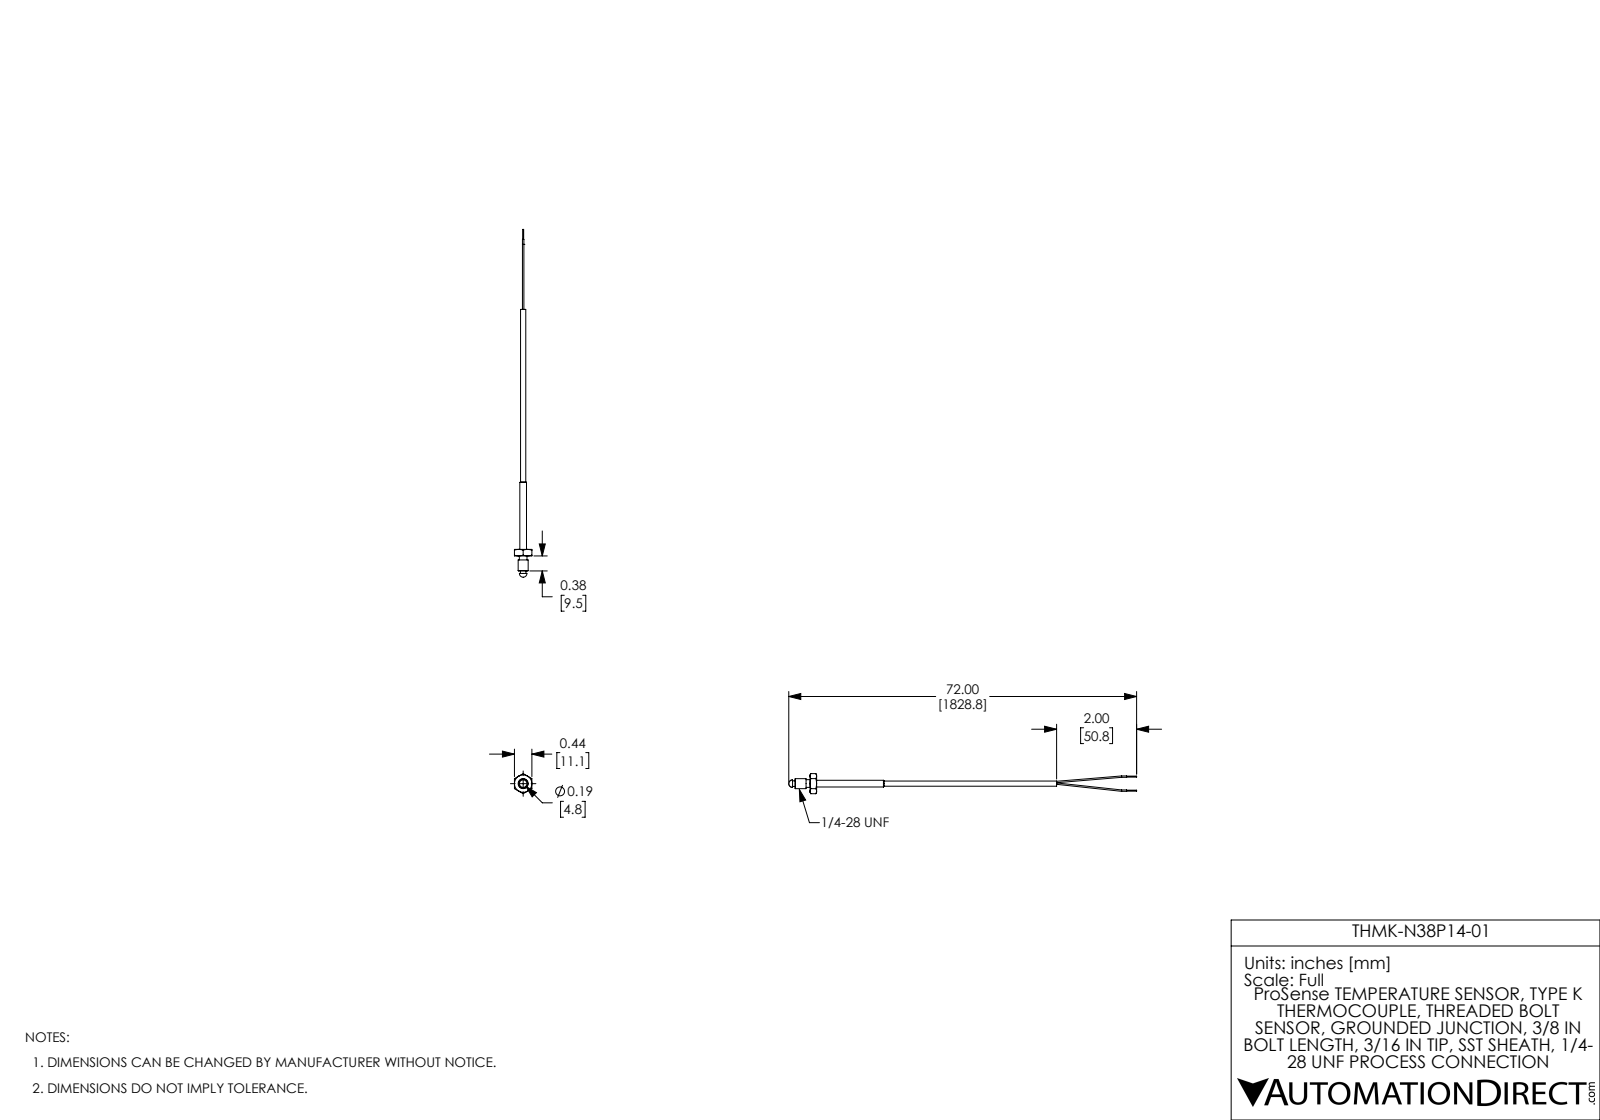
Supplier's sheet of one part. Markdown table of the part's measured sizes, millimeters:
| quantity | value |
| --- | --- |
| part name | THMK-N38P14-01 |
| STEP written by | SolidWorks 2017 (AUTOMOTIVE_DESIGN) |
| units | millimeters |
| bodies | 1 solid, 57 faces (17 planar, 18 cylindrical, 22 other) |
| overall size | 220.9 × 12.8 × 11.1 |
| volume | 2 360 mm³ |
| surface area | 2 596 mm² |
| round bosses / shafts (diameter × count) | 0.6 × 2, 6.4 × 1, 4.9 × 1, 4.3 × 1, 3.6 × 1, 3.3 × 1, 0.9 × 1, 0.9 × 1 |
| main face-to-face distances | 4.2, 11, 13.7, 9.5, 6.7, 2.5, 7, 15.3, 11.1, 8.6 |
